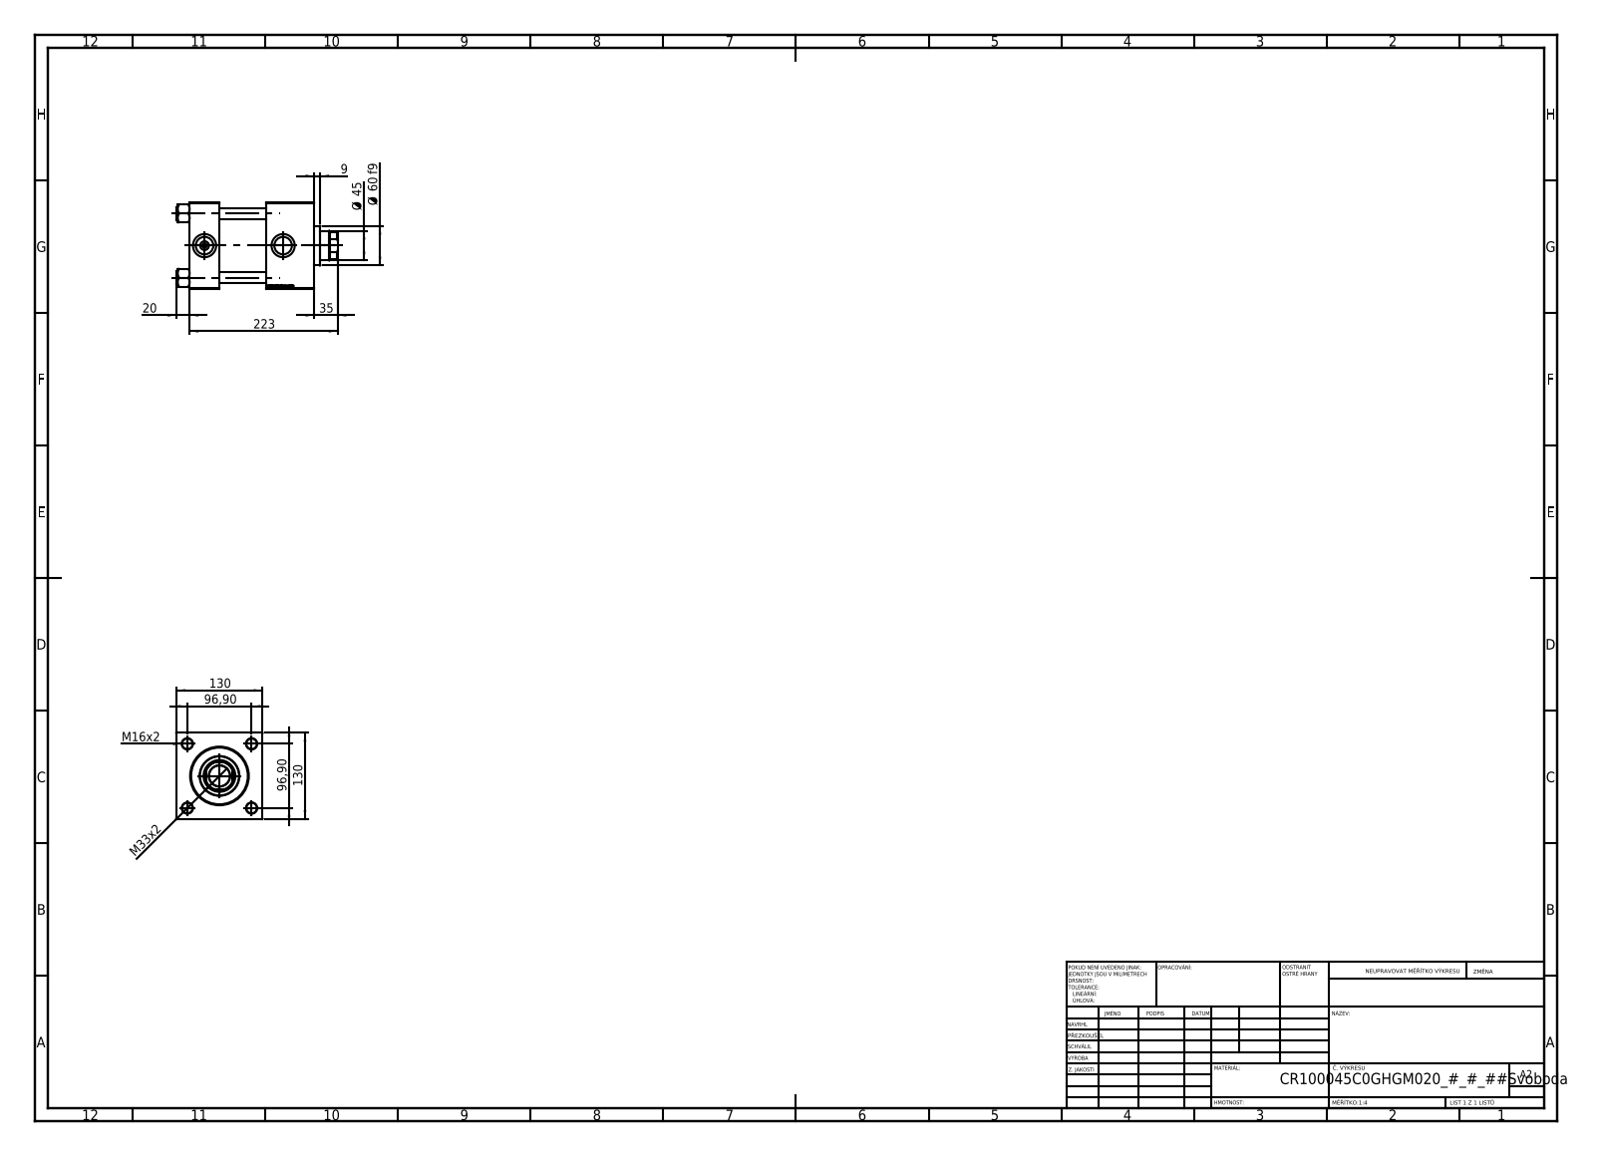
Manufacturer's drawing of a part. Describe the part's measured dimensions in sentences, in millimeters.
The part is named "V215_VC_A; NUT_M5_C; V215CR_VCP_C; V215CR_C_Body (+1 more)". Its 3-D file was written by "SolidWorks 2019 (CONFIG_CONTROL_DESIGN)". It is 11 solids with 1196 faces: 574 planar, 86 cylindrical and 536 other. Overall it measures 243 by 130 by 130 millimeters. Its volume is 2 425 000 cubic millimeters and its surface area 326 388 square millimeters. Round holes: 4 of diameter 16, 2 of diameter 7, 2 of diameter 26.44, 2 of diameter 35, 1 of diameter 31.5, 1 of diameter 45, 1 of diameter 48, 1 of diameter 76, 1 of diameter 85.5, 1 of diameter 100. Round bosses or shafts: 4 of diameter 19, 1 of diameter 106, 1 of diameter 60. Partial cylindrical surfaces (rounded edges, fillets, slot ends): 1 of radius 22. The main face-to-face distances are 130, 45, 188, 143, 116, 71, 72, 20, 96, 51. The hole center spacings are 68.52, 96.9, 137.04, 118.5.
